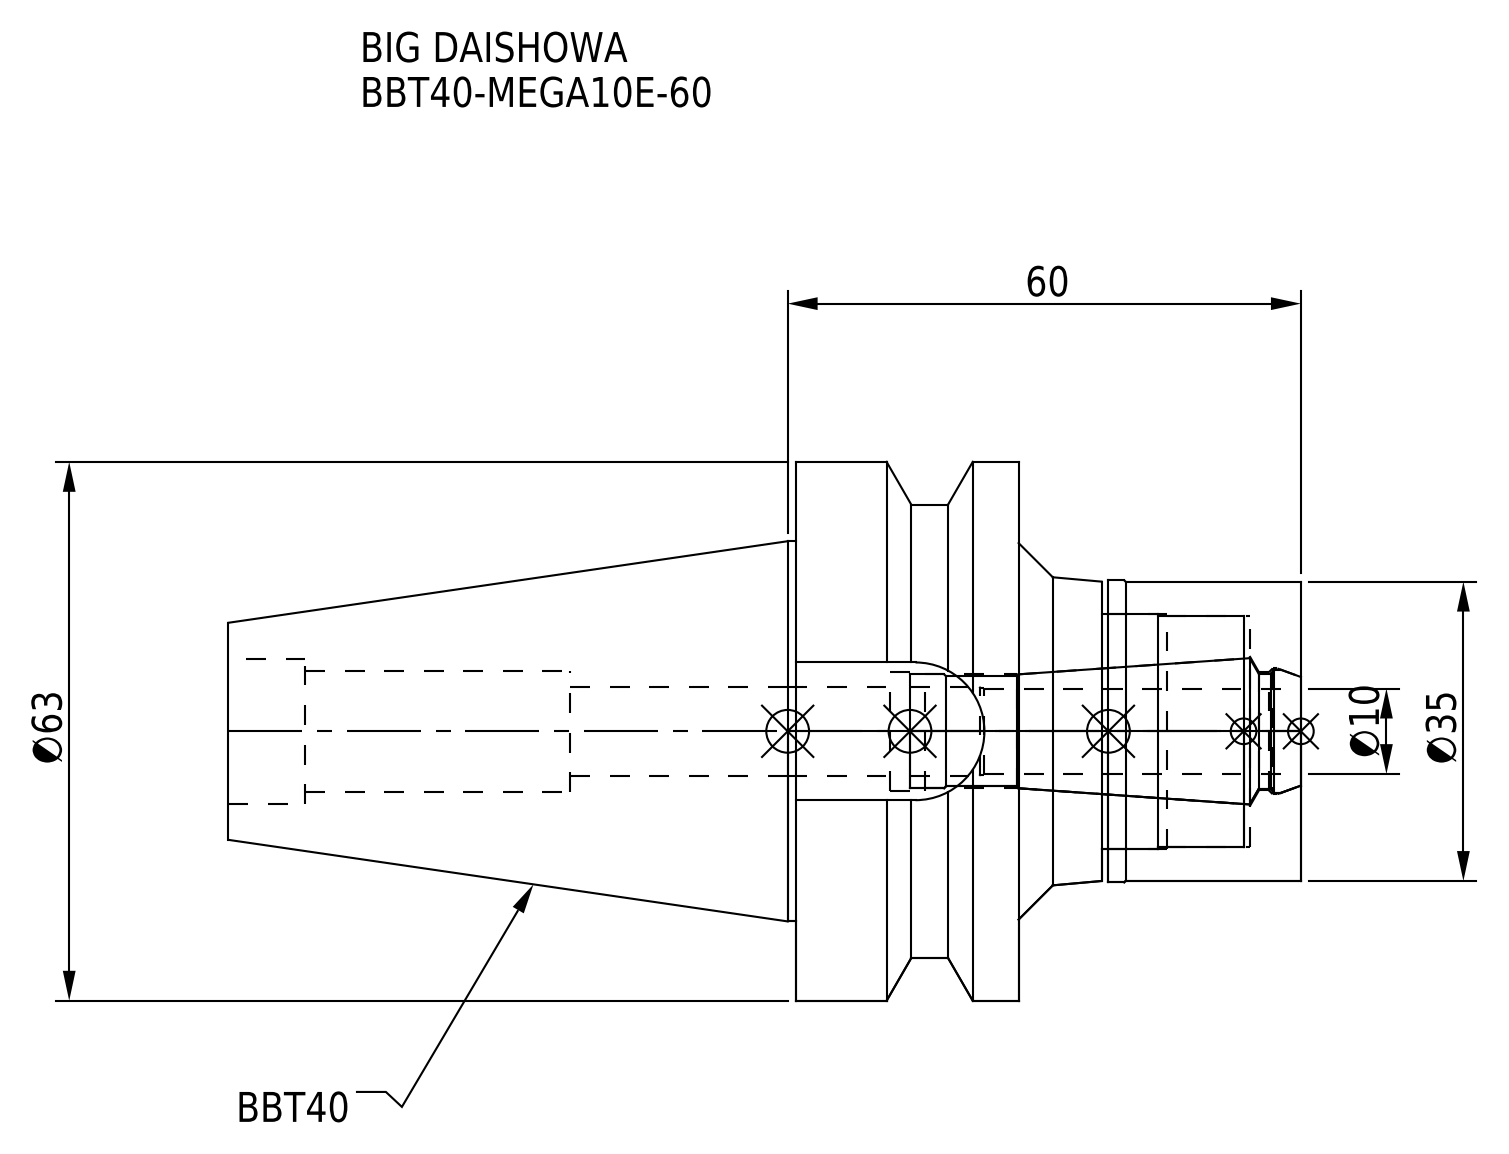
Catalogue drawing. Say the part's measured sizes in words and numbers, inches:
The part is named "BBT40-MEGA10E-60-100.stp; BBT40-MEGA10E-60; MEN10_1.stp; DXF_TEMP_ASSY_ASM_4_ASM.stp (+3 more)". Its 3-D file was written by "SolidWorks 2019 (CONFIG_CONTROL_DESIGN)". It is 2 solids with 78 faces: 20 planar, 38 cylindrical and 20 other. Overall it measures 4.937 by 2.48 by 2.48 inches. Its volume is 9.154 cubic inches and its surface area 48.93 square inches. Round holes: 1 of diameter 0.409, 1 of diameter 0.524, 1 of diameter 0.543, 1 of diameter 0.547, 1 of diameter 0.559, 1 of diameter 0.579, 1 of diameter 0.669, 1 of diameter 1.063, 1 of diameter 1.083. Round bosses or shafts: 1 of diameter 2.48, 1 of diameter 2.087, 1 of diameter 1.75, 1 of diameter 1.39, 1 of diameter 1.378. Partial cylindrical surfaces (rounded edges, fillets, slot ends): 1 of radius 0.317. The main face-to-face distances are 1.024, 1.299, 2.323, 0.382, 0.886, 0.413, 1.437, 0.917, 0.031, 1.406.
